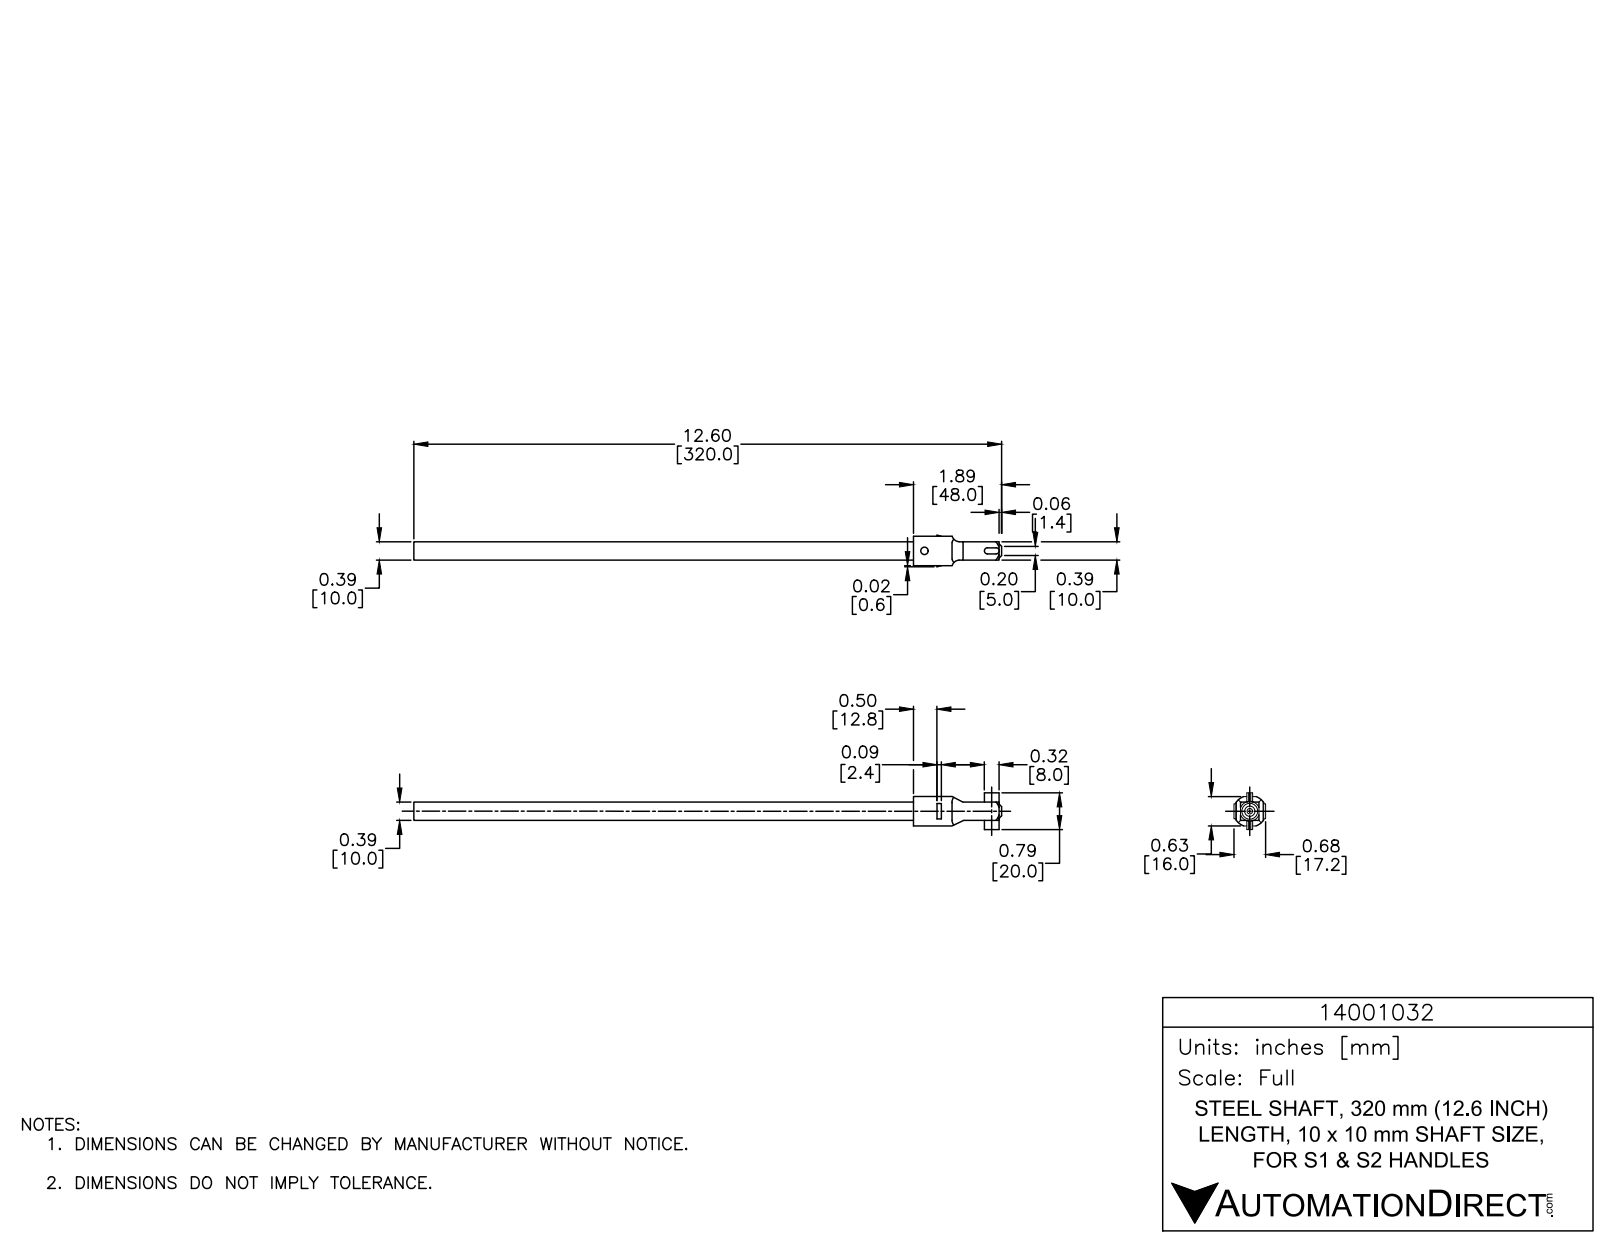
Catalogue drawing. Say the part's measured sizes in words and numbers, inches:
The part is named "14001032". Its 3-D file was written by "SolidWorks 2015 (AUTOMOTIVE_DESIGN)". It is 1 solid with 72 faces: 35 planar, 24 cylindrical and 13 other. Overall it measures 12.598 by 0.787 by 0.677 inches. Its volume is 2.032 cubic inches and its surface area 19.45 square inches. Round bosses or shafts: 1 of diameter 0.118. Partial cylindrical surfaces (rounded edges, fillets, slot ends): 4 of radius 0.012, 4 of radius 0.118, 2 of radius 0.039, 2 of radius 0.335, 1 of radius 0.063, 1 of radius 0.236. The main face-to-face distances are 0.394, 0.102, 0.496, 0.512, 0.118, 0.598, 0.63, 0.236, 0.362, 0.134.
